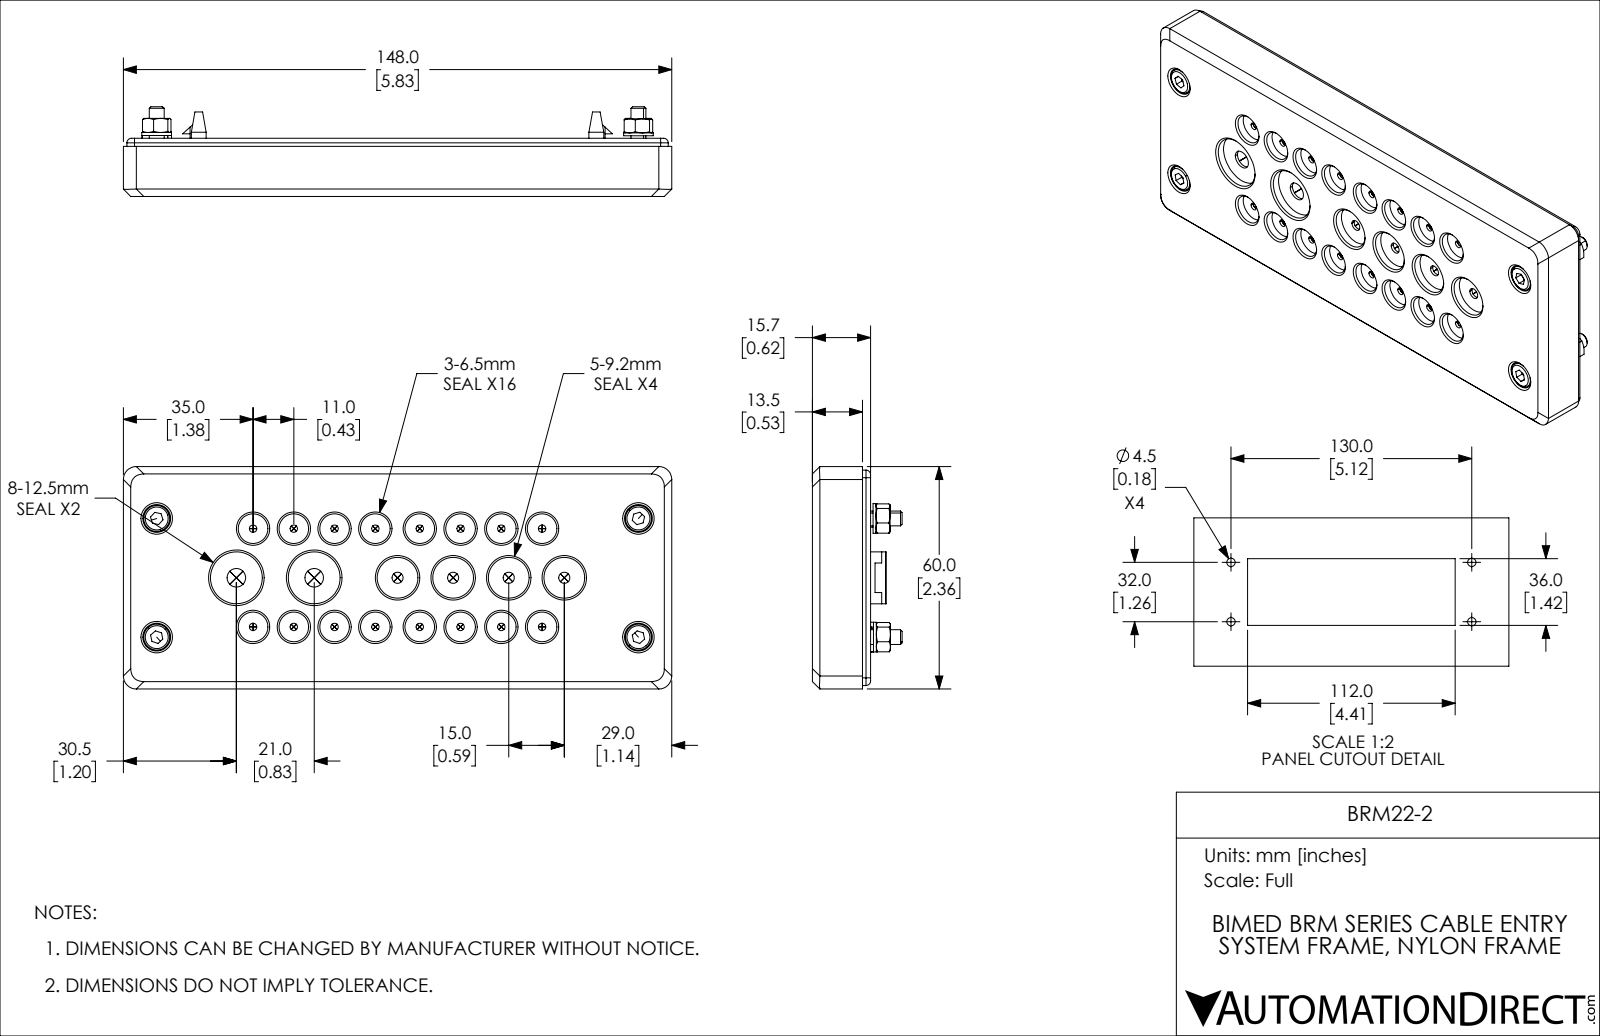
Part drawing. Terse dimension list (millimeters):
name: BRM22-2
written by: SolidWorks 2021 (CONFIG_CONTROL_DESIGN)
unit: mm
bodies: 18 solids, 1433 faces (449 planar, 678 cylindrical, 306 other)
size: 148 × 60 × 24.2
volume: 90 384 mm³; area: 90 889 mm²
holes: 21× ⌀2.8, 20× ⌀2, 20× ⌀7.5, 16× ⌀8, 16× ⌀9.7, 4× ⌀3, 4× ⌀3.24, 4× ⌀4.3, 4× ⌀4.5, 4× ⌀10.5, 4× ⌀11, 4× ⌀13.5
bosses: 20× ⌀2.5, 8× ⌀4, 4× ⌀8, 4× ⌀7
rounds: 28× R1, 16× R3.25, 8× R1.25, 8× R5, 6× R0.5, 4× R2, 4× R2.05, 4× R3.5
face distances: 0.8, 2, 2.8, 3, 5, 5.8, 2.5, 3.3, 8.3, 5.3
hole spacings: 11, 28.69, 45, 21.55, 22, 26.5, 30.98, 34.44
